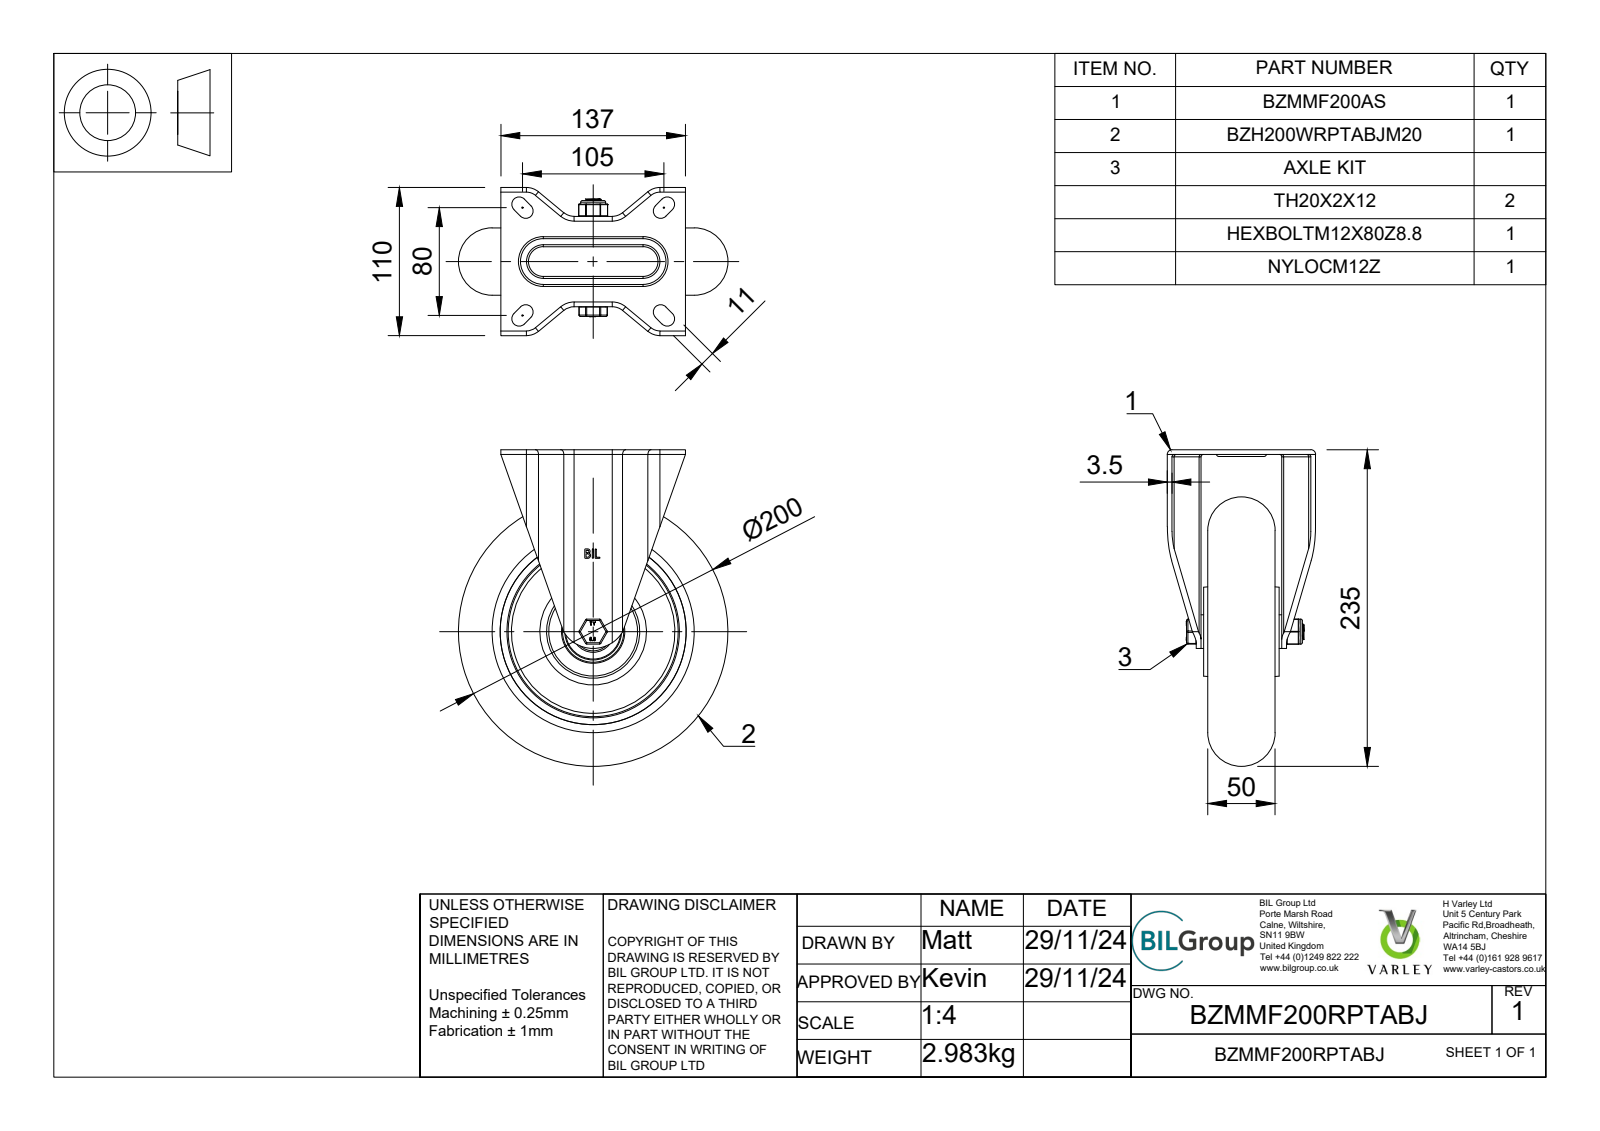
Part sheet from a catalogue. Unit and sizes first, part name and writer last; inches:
Units: inches
Overall size (bounding box): 9.252 × 7.874 × 4.331
Round holes (diameter × count): ⌀0.354 ×12, ⌀0.472 ×1, ⌀0.48 ×1, ⌀0.551 ×1, ⌀0.787 ×1, ⌀1.122 ×1, ⌀1.213 ×1, ⌀1.587 ×1, ⌀1.594 ×1, ⌀1.654 ×1, ⌀1.85 ×1, ⌀5.433 ×1
Round bosses / shafts (diameter × count): ⌀0.354 ×12, ⌀1.606 ×1, ⌀1.232 ×1, ⌀1.063 ×1, ⌀0.984 ×1, ⌀0.945 ×1, ⌀0.78 ×1, ⌀0.728 ×1
Partial cylindrical surfaces — rounded edges, fillets, slot ends (radius × count): R0.02 ×18, R0.039 ×12, R0.059 ×8, R0.069 ×8, R0.138 ×8, R0.217 ×8, R0.236 ×4, R0.276 ×4
Main face-to-face distances: 0.138, 1.063, 1.437, 0.236, 0.374, 0.925, 0.197, 1.102, 1.299, 0.969
Hole centre spacings: 3.012, 1.559, 4.259, 5.819, 5.217, 5.217, 6.024, 6.024
Volume: 73.41 in³ · Surface area: 482.9 in²
Bodies: 35 solids, 1122 faces (426 planar, 250 cylindrical, 446 other)
Part name (STEP PRODUCT): BZMMF200RPTABJ v3; BZMMF200AS v1; BZMMF200AS; ZINC PLATED, PRESSED STEEL BRACKET (+8 more)
STEP written by: Autodesk Translation Framework v13.20.0.188 (AP242_MANAGED_MODEL_BASED_3D_ENGINEERING_MIM_LF)
